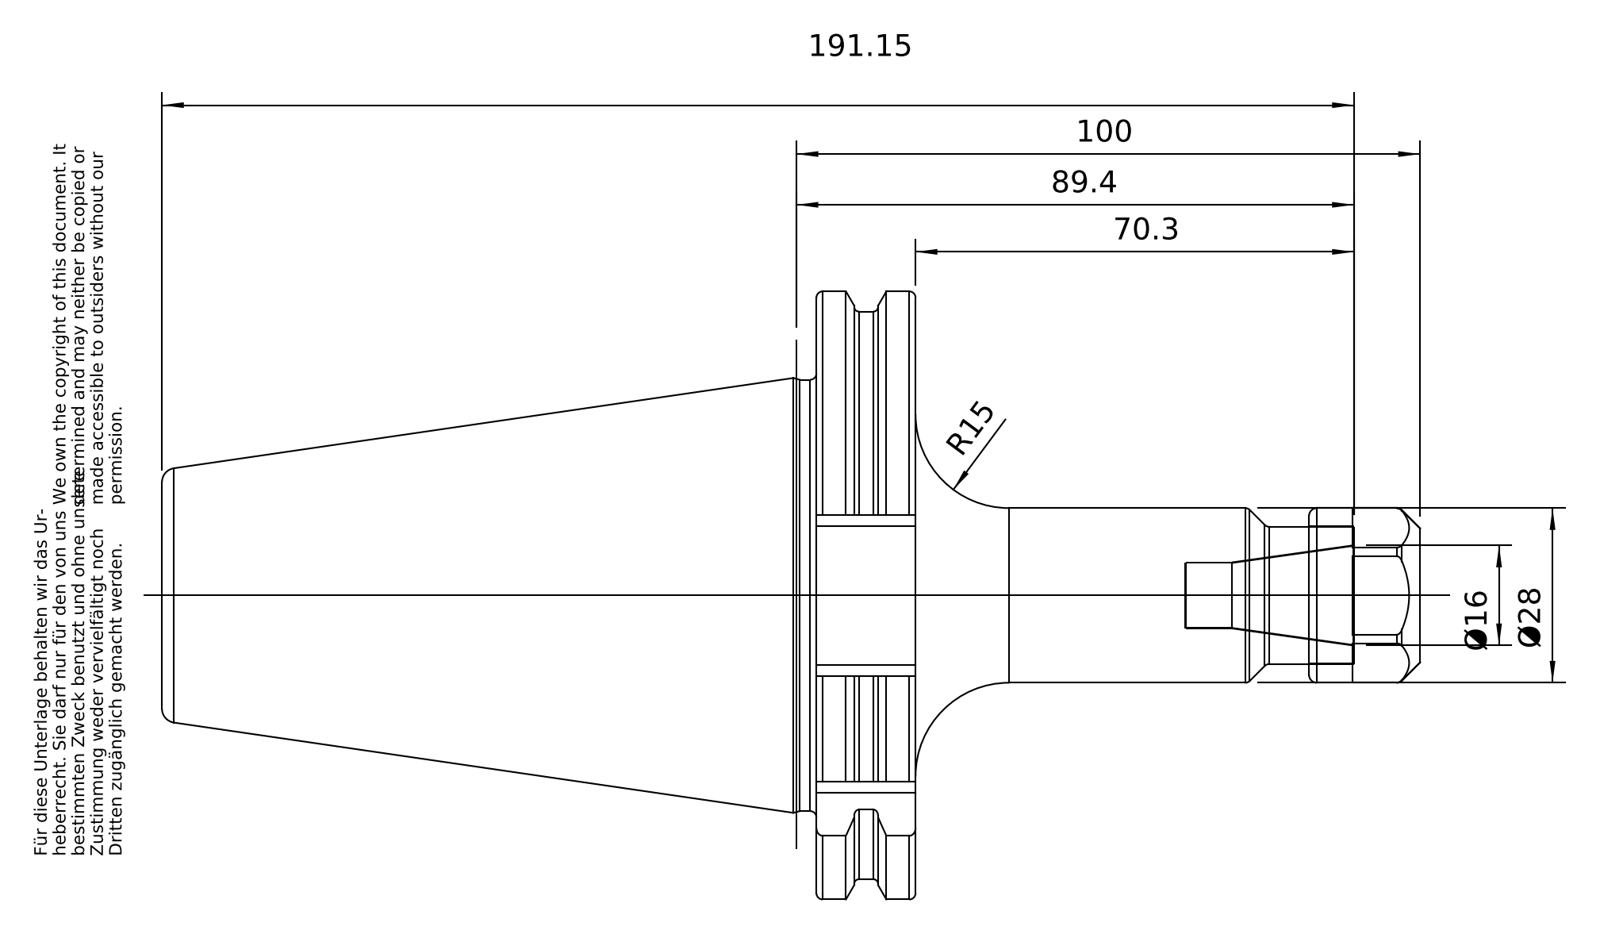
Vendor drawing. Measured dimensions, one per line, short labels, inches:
name: 50-321-16; 83-912-16; 50-321-16_ASM
written by: PRO/ENGINEER BY PARAMETRIC TECHNOLOGY CORPORATION, 2010430 (CONFIG_CONTROL_DESIGN)
unit: in
bodies: 2 solids, 129 faces (29 planar, 32 cylindrical, 68 other)
size: 7.937 × 3.837 × 3.701
volume: 23.85 in³; area: 79.7 in²
holes: 1× ⌀0.413, 1× ⌀0.817, 1× ⌀0.985, 1× ⌀1.012
bosses: 1× ⌀3.583, 1× ⌀2.722, 1× ⌀1.102, 1× ⌀0.945, 1× ⌀0.866
rounds: 5× R0.069, 1× R1.919
face distances: 0.624, 3.11, 2.486, 4.126, 4.75, 7.236, 0.984, 7.937, 3.811, 3.187
